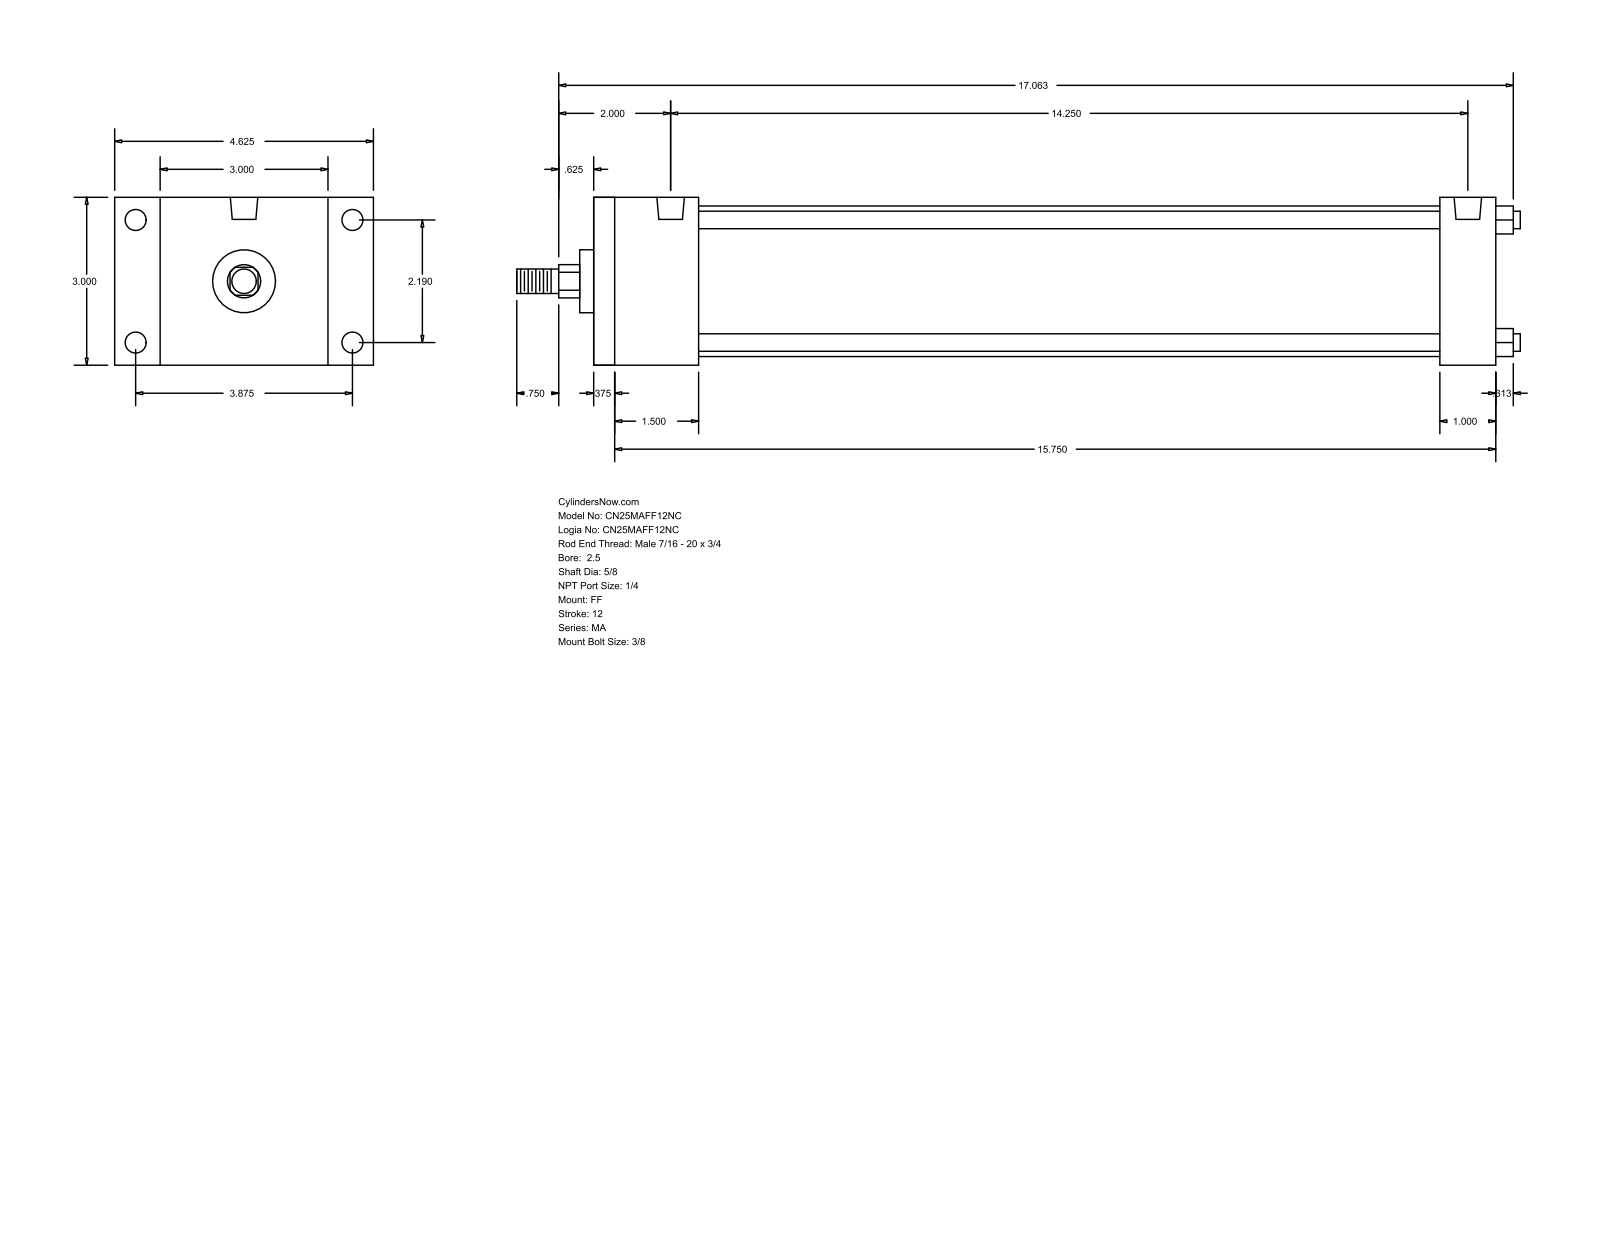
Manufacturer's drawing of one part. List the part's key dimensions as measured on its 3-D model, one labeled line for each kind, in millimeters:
Part name (STEP PRODUCT): MA_FF__0250_0.625
STEP written by: GSSL Pune (CONFIG_CONTROL_DESIGN)
Units: millimetres
Bodies: 0 solids, 92 faces (64 planar, 28 cylindrical, 0 other)
Overall size (bounding box): 455.61 × 117.47 × 76.2
Round holes (diameter × count): ⌀7.94 ×4, ⌀9.53 ×4, ⌀12.49 ×2
Round bosses / shafts (diameter × count): ⌀7.94 ×4, ⌀68.33 ×1, ⌀28.57 ×1, ⌀15.88 ×1, ⌀11.11 ×1
Partial cylindrical surfaces — rounded edges, fillets, slot ends (radius × count): R7.54 ×1
Main face-to-face distances: 76.2, 409.57, 400.05, 9.52, 25.4, 47.62, 384.17, 38.1, 374.65, 336.55
Hole centre spacings: 55.62, 98.42, 113.05, 361.95
